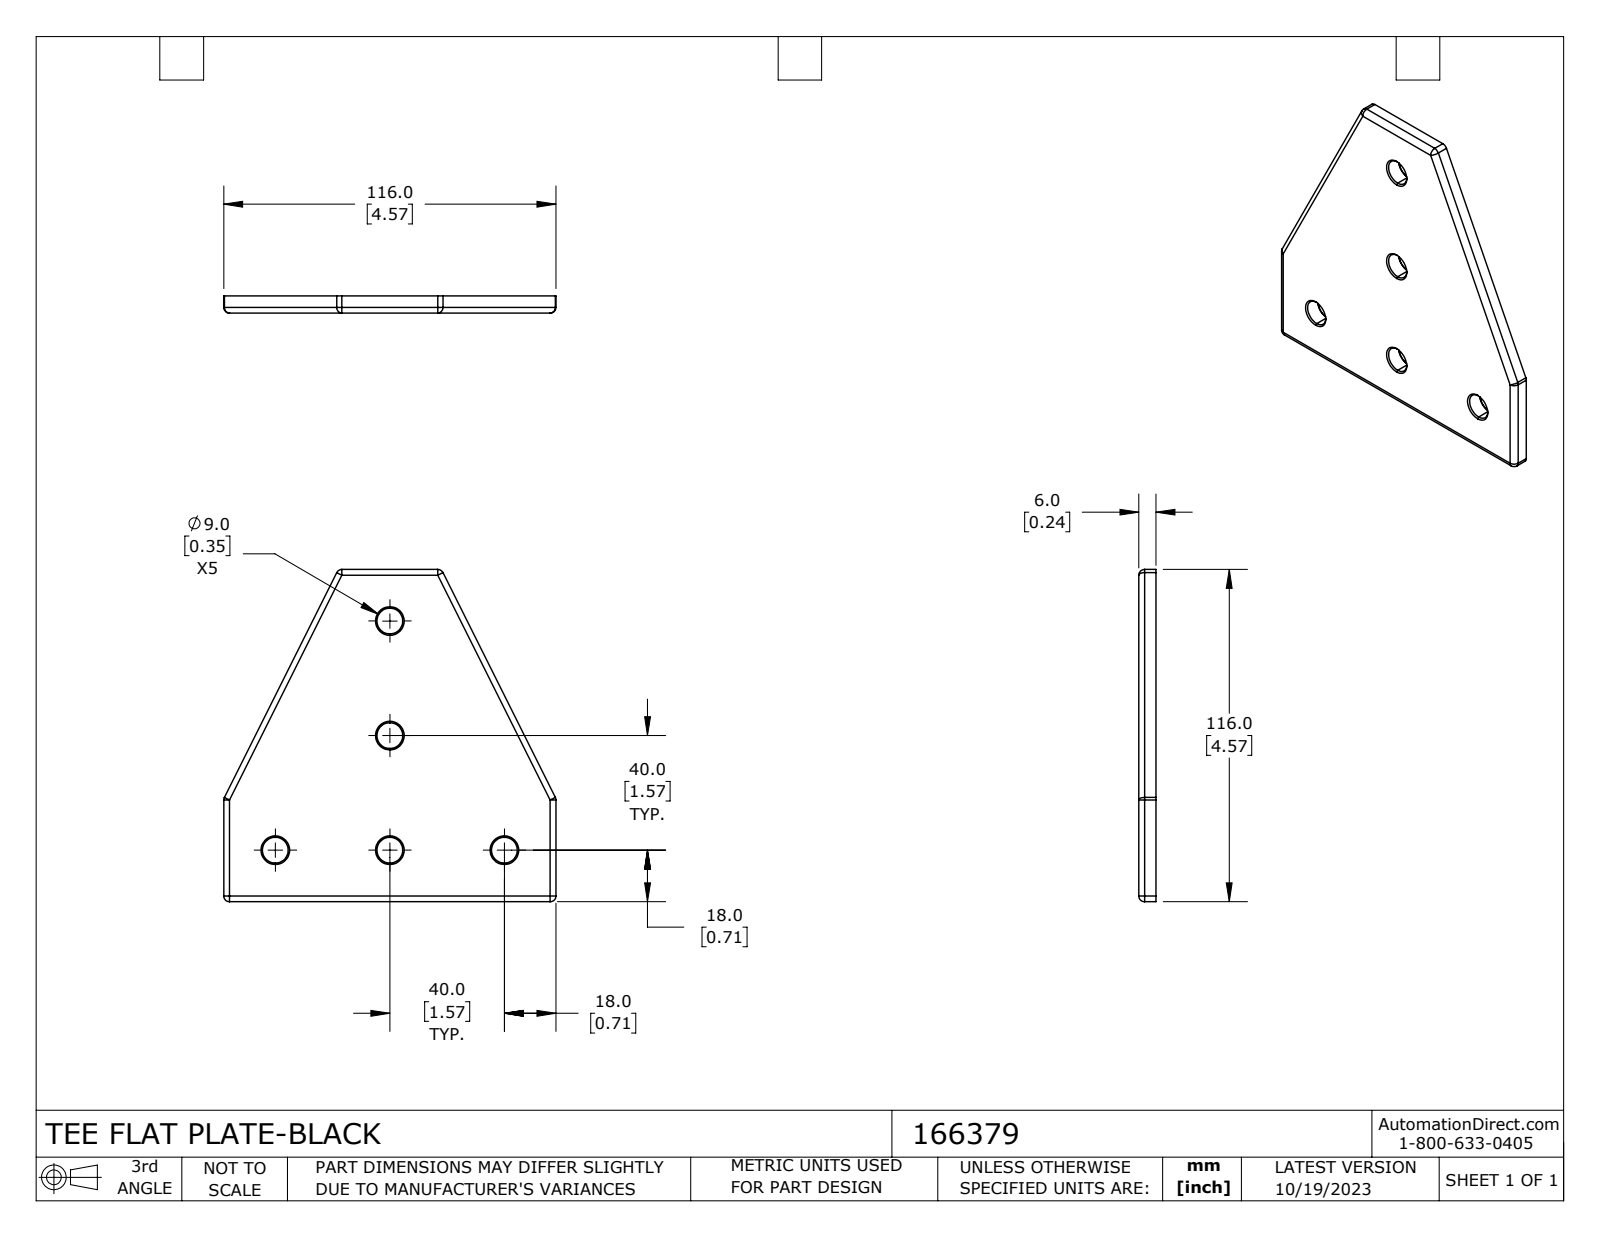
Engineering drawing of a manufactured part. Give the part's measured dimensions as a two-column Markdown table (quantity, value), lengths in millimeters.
| quantity | value |
| --- | --- |
| part name | 166379 |
| STEP written by | SolidWorks 2023 (CONFIG_CONTROL_DESIGN) |
| units | millimeters |
| bodies | 1 solid, 56 faces (8 planar, 22 cylindrical, 26 other) |
| overall size | 116 × 116 × 6 |
| volume | 59 236 mm³ |
| surface area | 22 698 mm² |
| round holes (diameter × count) | 9 × 5 |
| partial cylindrical surfaces (radius × count) | 2 × 12 |
| main face-to-face distances | 6, 116 |
| hole center spacings | 40, 56.57, 80, 89.44 |
